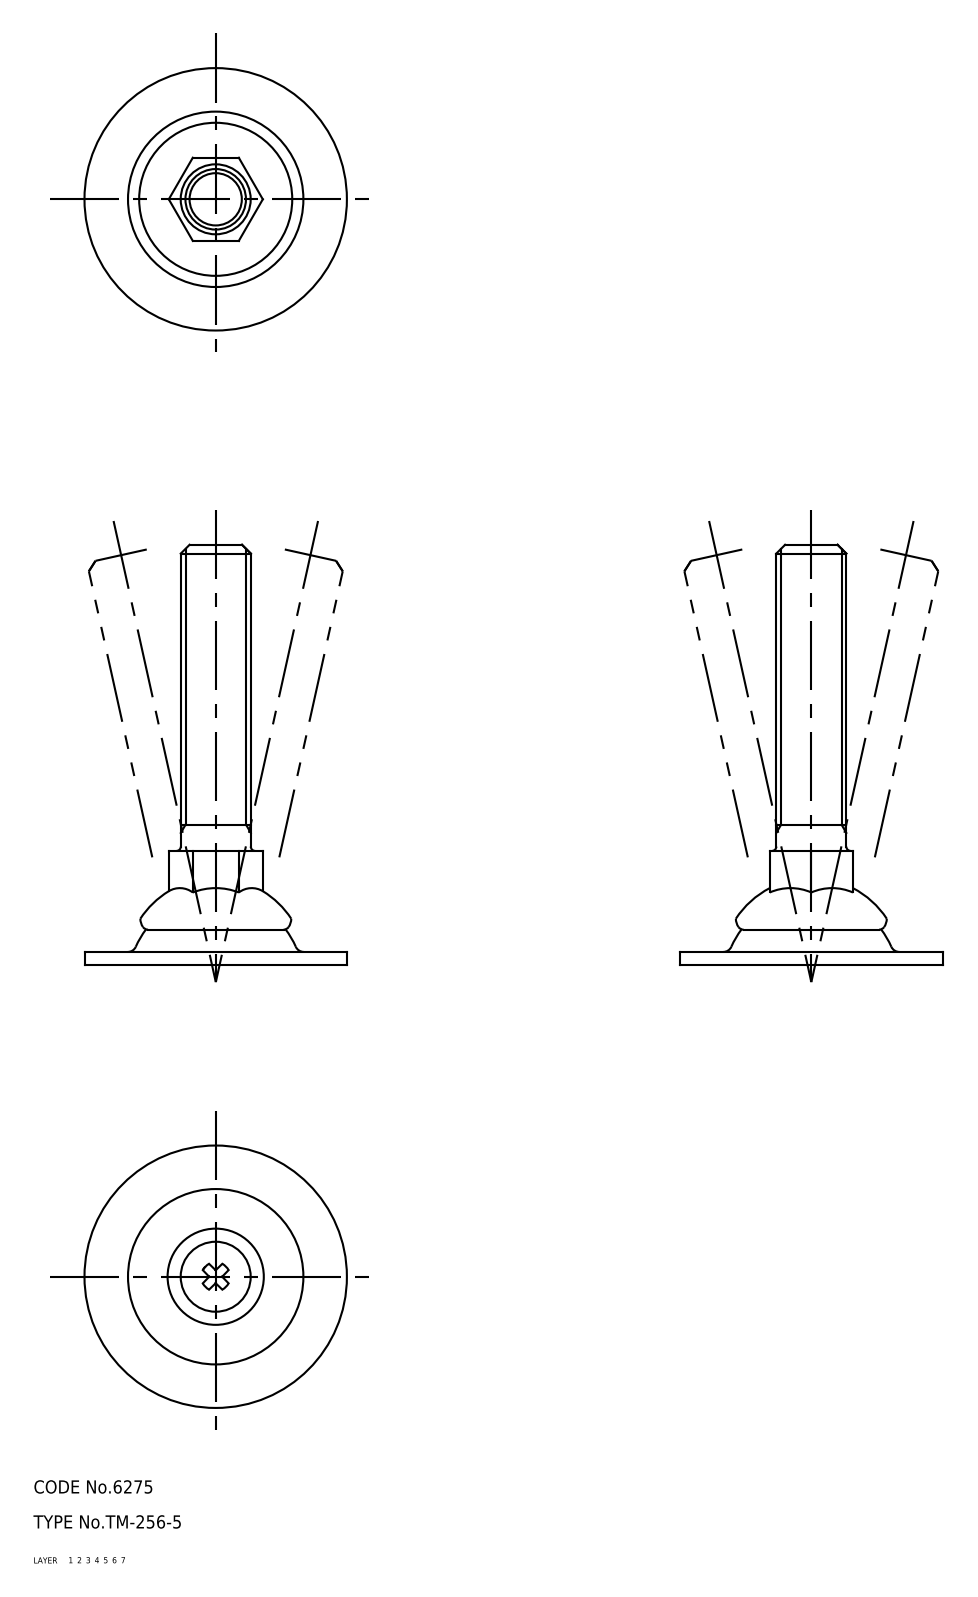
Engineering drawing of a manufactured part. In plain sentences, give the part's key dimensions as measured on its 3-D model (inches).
The part is named "67113093; 67113106; 67113119; 67113132". Its 3-D file was written by "CADfix (AUTOMOTIVE_DESIGN)". It is 4 solids with 69 faces: 0 planar, 0 cylindrical and 69 other. Overall it measures 3.78 by 2.362 by 2.362 inches. Its volume is 1.803 cubic inches and its surface area 23.36 square inches.
